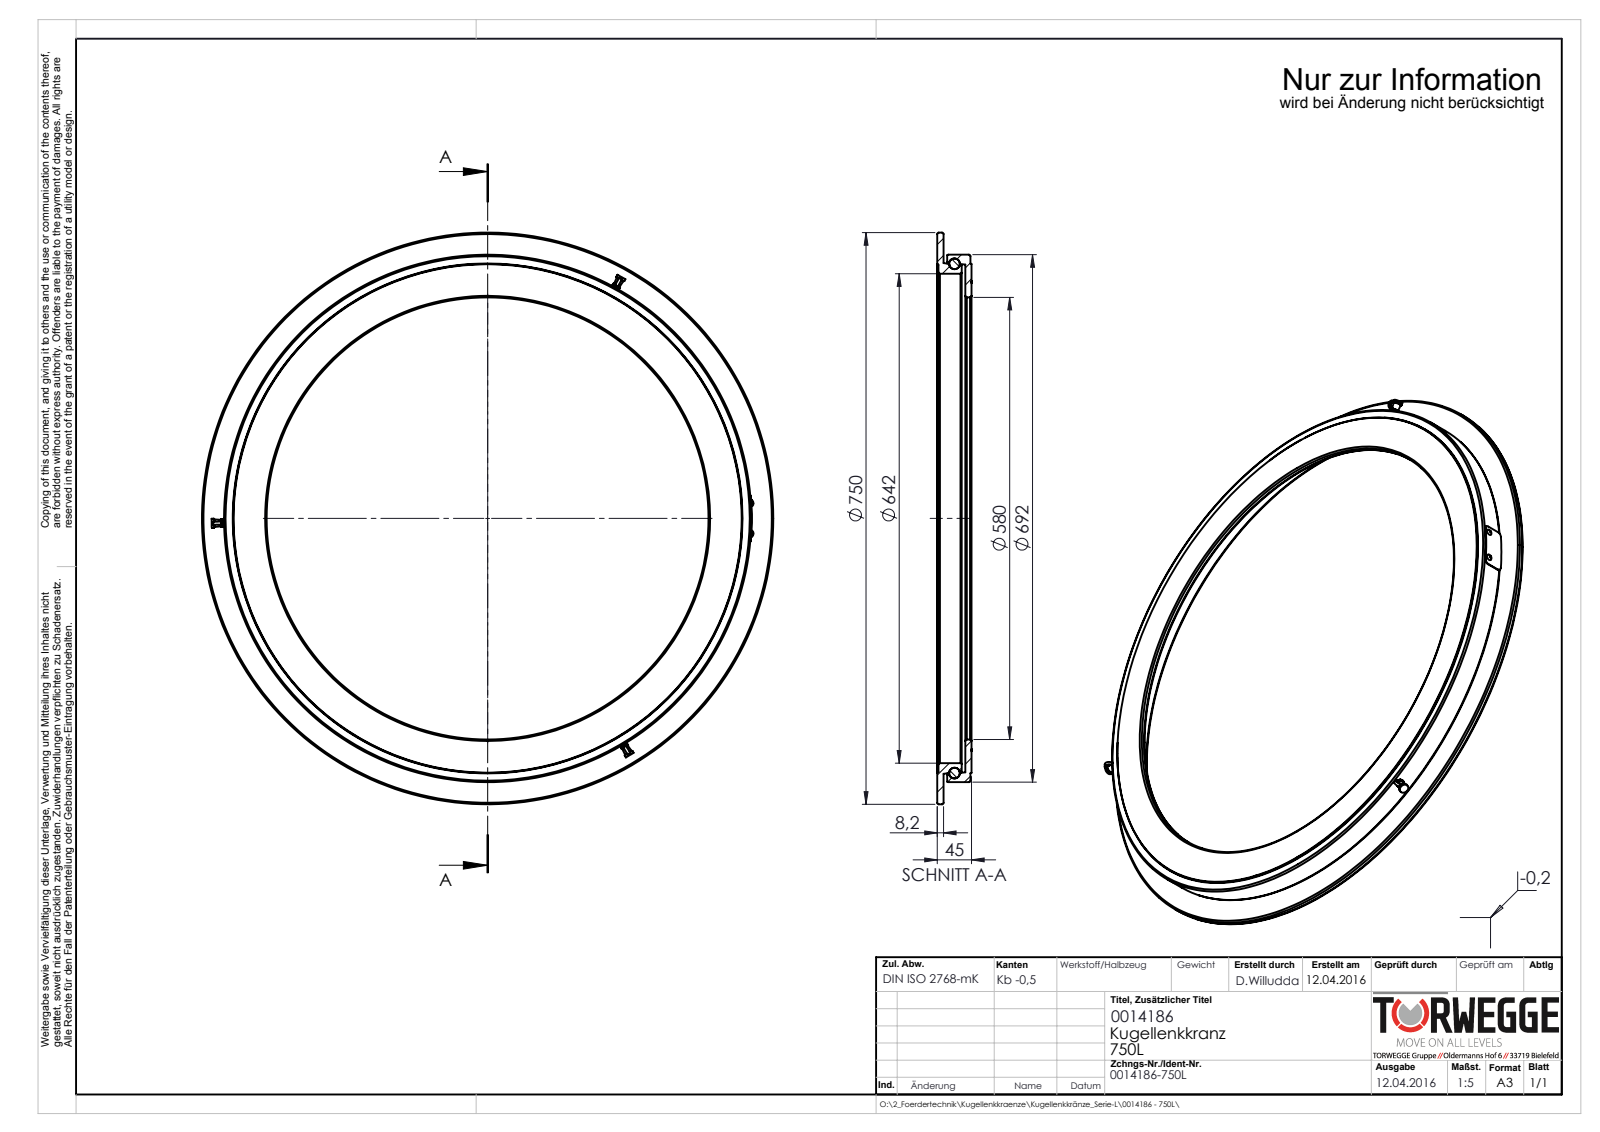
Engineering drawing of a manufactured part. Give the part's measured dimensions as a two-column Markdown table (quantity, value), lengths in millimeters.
| quantity | value |
| --- | --- |
| part name | 0014186-750L; JS-1101-021; 000017003; KLK-1300-038 (+4 more) |
| STEP written by | SolidWorks 2016 (AUTOMOTIVE_DESIGN) |
| units | millimeters |
| bodies | 159 solids, 633 faces (80 planar, 108 cylindrical, 445 other) |
| overall size | 750 × 750 × 45.08 |
| volume | 2 930 000 mm³ |
| surface area | 830 389 mm² |
| round holes (diameter × count) | 1.5 × 5, 6 × 5, 4 × 3, 7.5 × 3, 4.9 × 2, 5.5 × 2, 14.5 × 1, 580 × 1, 642 × 1, 666 × 1 |
| round bosses / shafts (diameter × count) | 12 × 3, 7.5 × 3, 4.9 × 2, 4.7 × 2, 750 × 1, 692 × 1, 668 × 1, 14.1 × 1 |
| partial cylindrical surfaces (radius × count) | 5 × 7, 1.75 × 3, 4.62 × 3, 5.62 × 3, 346.75 × 1 |
| main face-to-face distances | 8.2, 36.8, 45, 28.6, 13, 32, 4.8, 23.8, 1.5, 43.5 |
